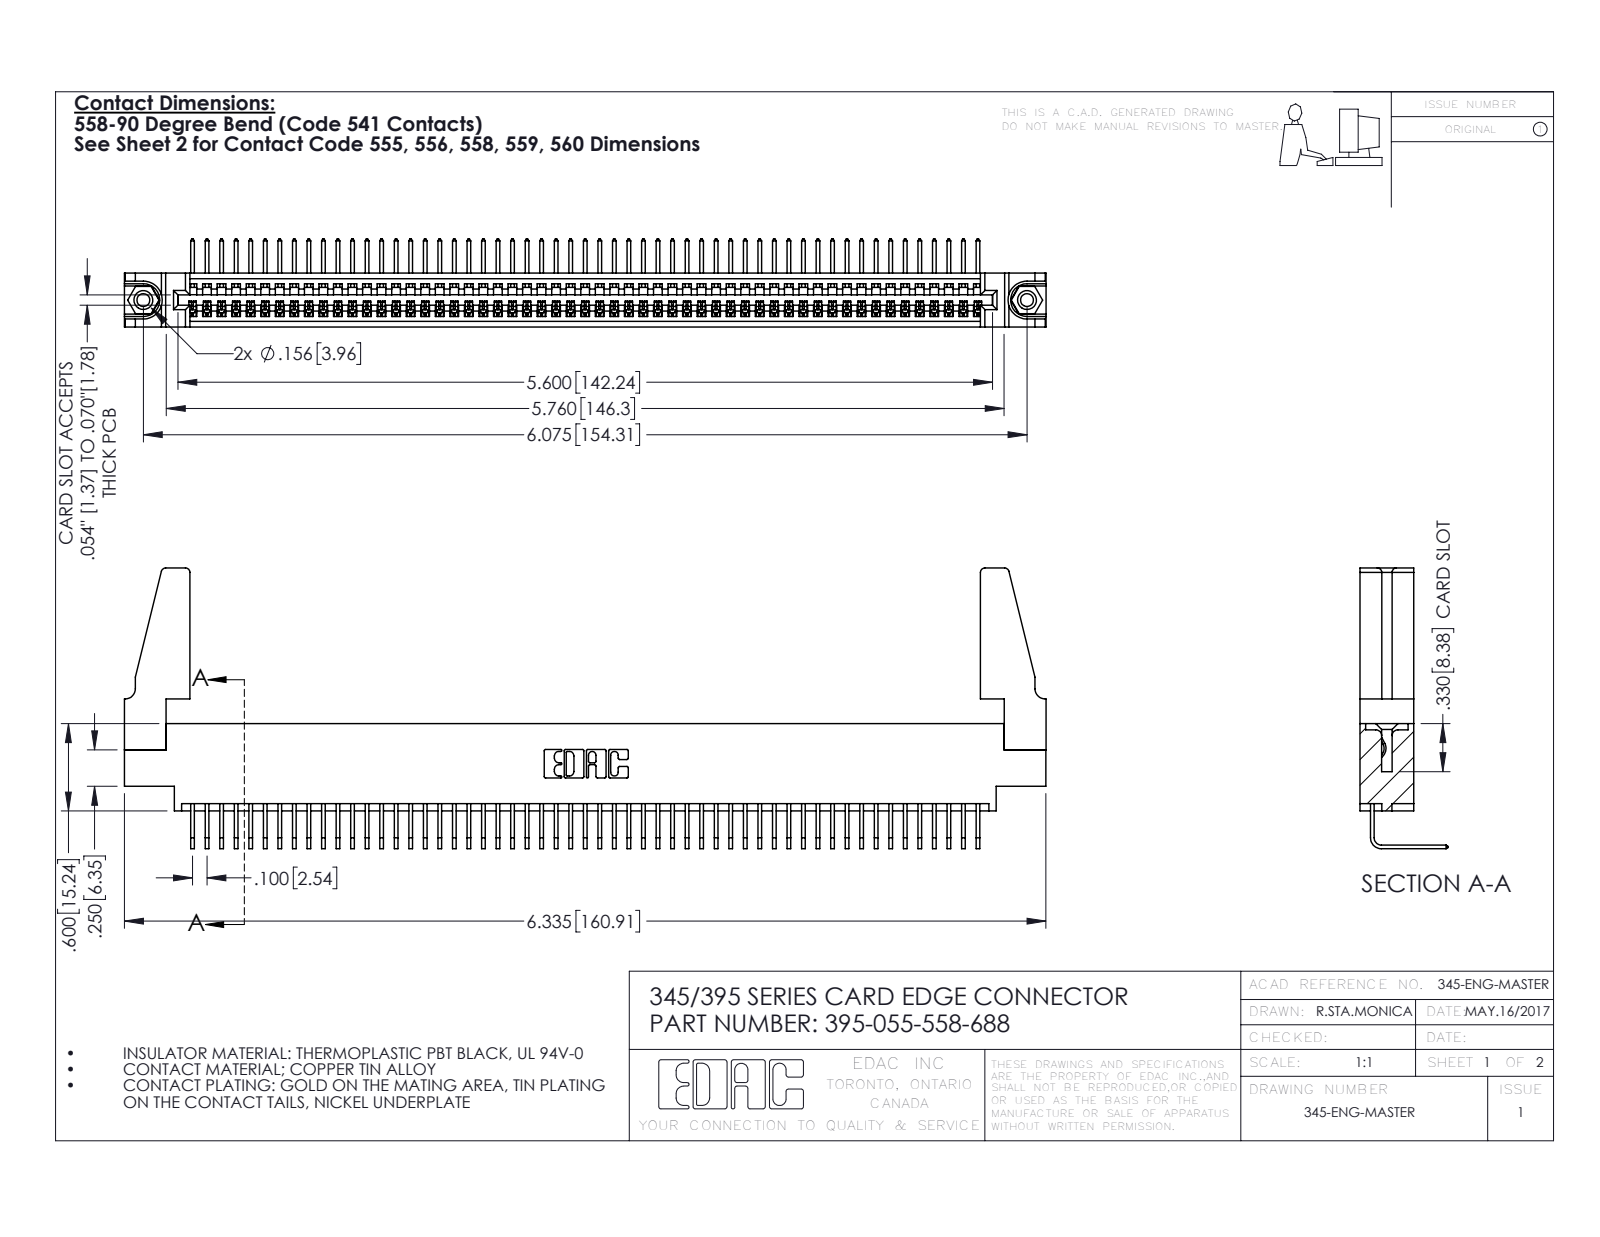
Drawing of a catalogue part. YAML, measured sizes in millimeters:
part_name: "345-220-078_345-220-088; 345-292-001_558 Tail - 2; 345-250-001_345-250-001-102; 345 Part_0.170 Offset - 0.156 Dia-TH (+1 more)"
step_written_by: "SolidWorks 2016 (CONFIG_CONTROL_DESIGN)"
units: millimeters
bodies: {solids: 60, faces: 3554, planar: 2466, cylindrical: 1072, other: 16}
overall_size: [160.9, 49, 15.4]
volume: 18710
surface_area: 25060
round_holes:
  - {diameter: 2.3, count: 2}
  - {diameter: 3.2, count: 2}
  - {diameter: 4, count: 2}
  - {diameter: 1.6, count: 1}
round_bosses_or_shafts:
  - {diameter: 3.9, count: 2}
partial_cylinders:
  - {radius: 0.2, count: 110}
  - {radius: 0.3, count: 22}
  - {radius: 0.8, count: 8}
  - {radius: 0.2, count: 6}
  - {radius: 0.8, count: 6}
  - {radius: 0.7, count: 3}
  - {radius: 0.8, count: 2}
  - {radius: 1, count: 2}
face_to_face_distances: [1.8, 7.6, 9.4, 5.1, 2.5, 6.9, 0.6, 5.7, 4.4, 3.8]
hole_center_spacings: [6.9, 148.3, 154.3]
